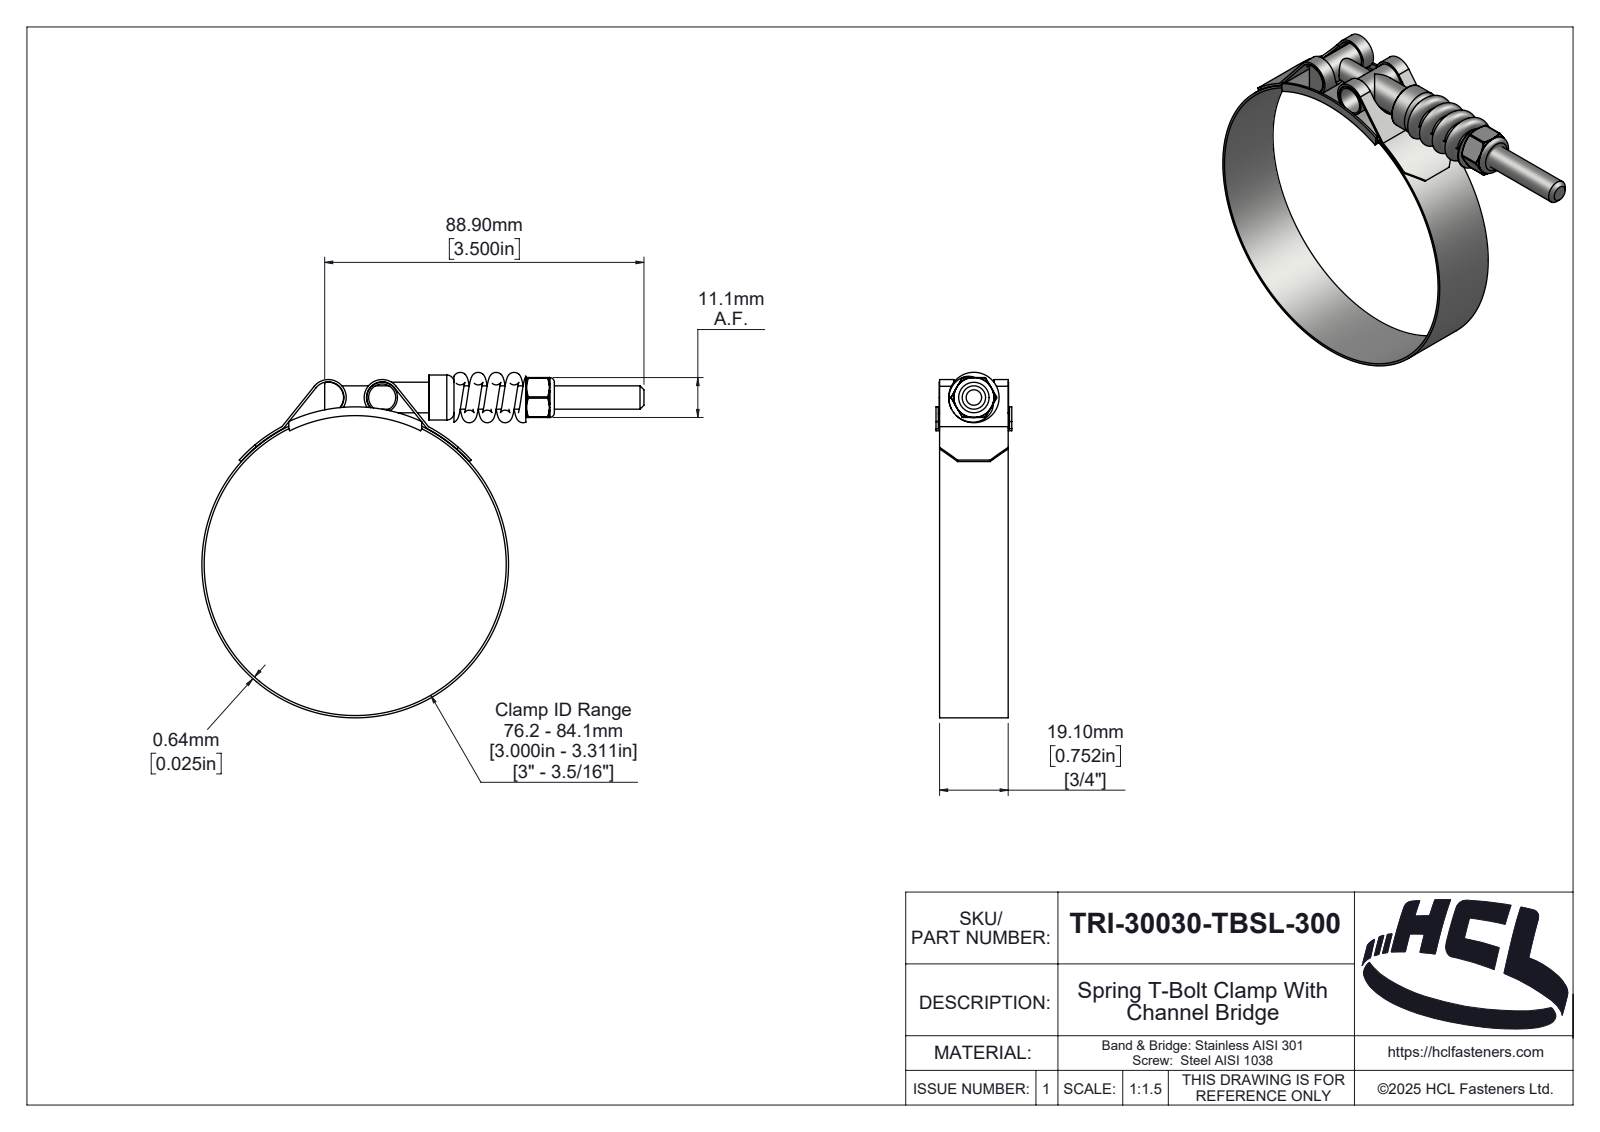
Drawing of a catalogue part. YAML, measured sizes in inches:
part_name: "TRI-30030-TBSL-300"
step_written_by: "SolidWorks 2025 (AUTOMOTIVE_DESIGN)"
units: inches
bodies: {solids: 7, faces: 336, planar: 48, cylindrical: 126, other: 162}
overall_size: [4.885, 3.786, 0.831]
volume: 0.668
surface_area: 32.96
round_holes:
  - {diameter: 0.213, count: 1}
  - {diameter: 0.25, count: 1}
  - {diameter: 0.256, count: 1}
  - {diameter: 0.296, count: 1}
  - {diameter: 3.311, count: 1}
round_bosses_or_shafts:
  - {diameter: 0.335, count: 2}
  - {diameter: 3.361, count: 1}
  - {diameter: 0.493, count: 1}
partial_cylinders:
  - {radius: 0.015, count: 6}
  - {radius: 0.02, count: 2}
  - {radius: 0.172, count: 2}
  - {radius: 0.197, count: 2}
  - {radius: 0.22, count: 2}
  - {radius: 0.023, count: 1}
  - {radius: 0.095, count: 1}
  - {radius: 0.119, count: 1}
face_to_face_distances: [0.025, 0.752, 0.039, 0.791, 0.806, 0.014, 0.766, 2.205, 0.437, 0.035]
hole_center_spacings: [1.852]
